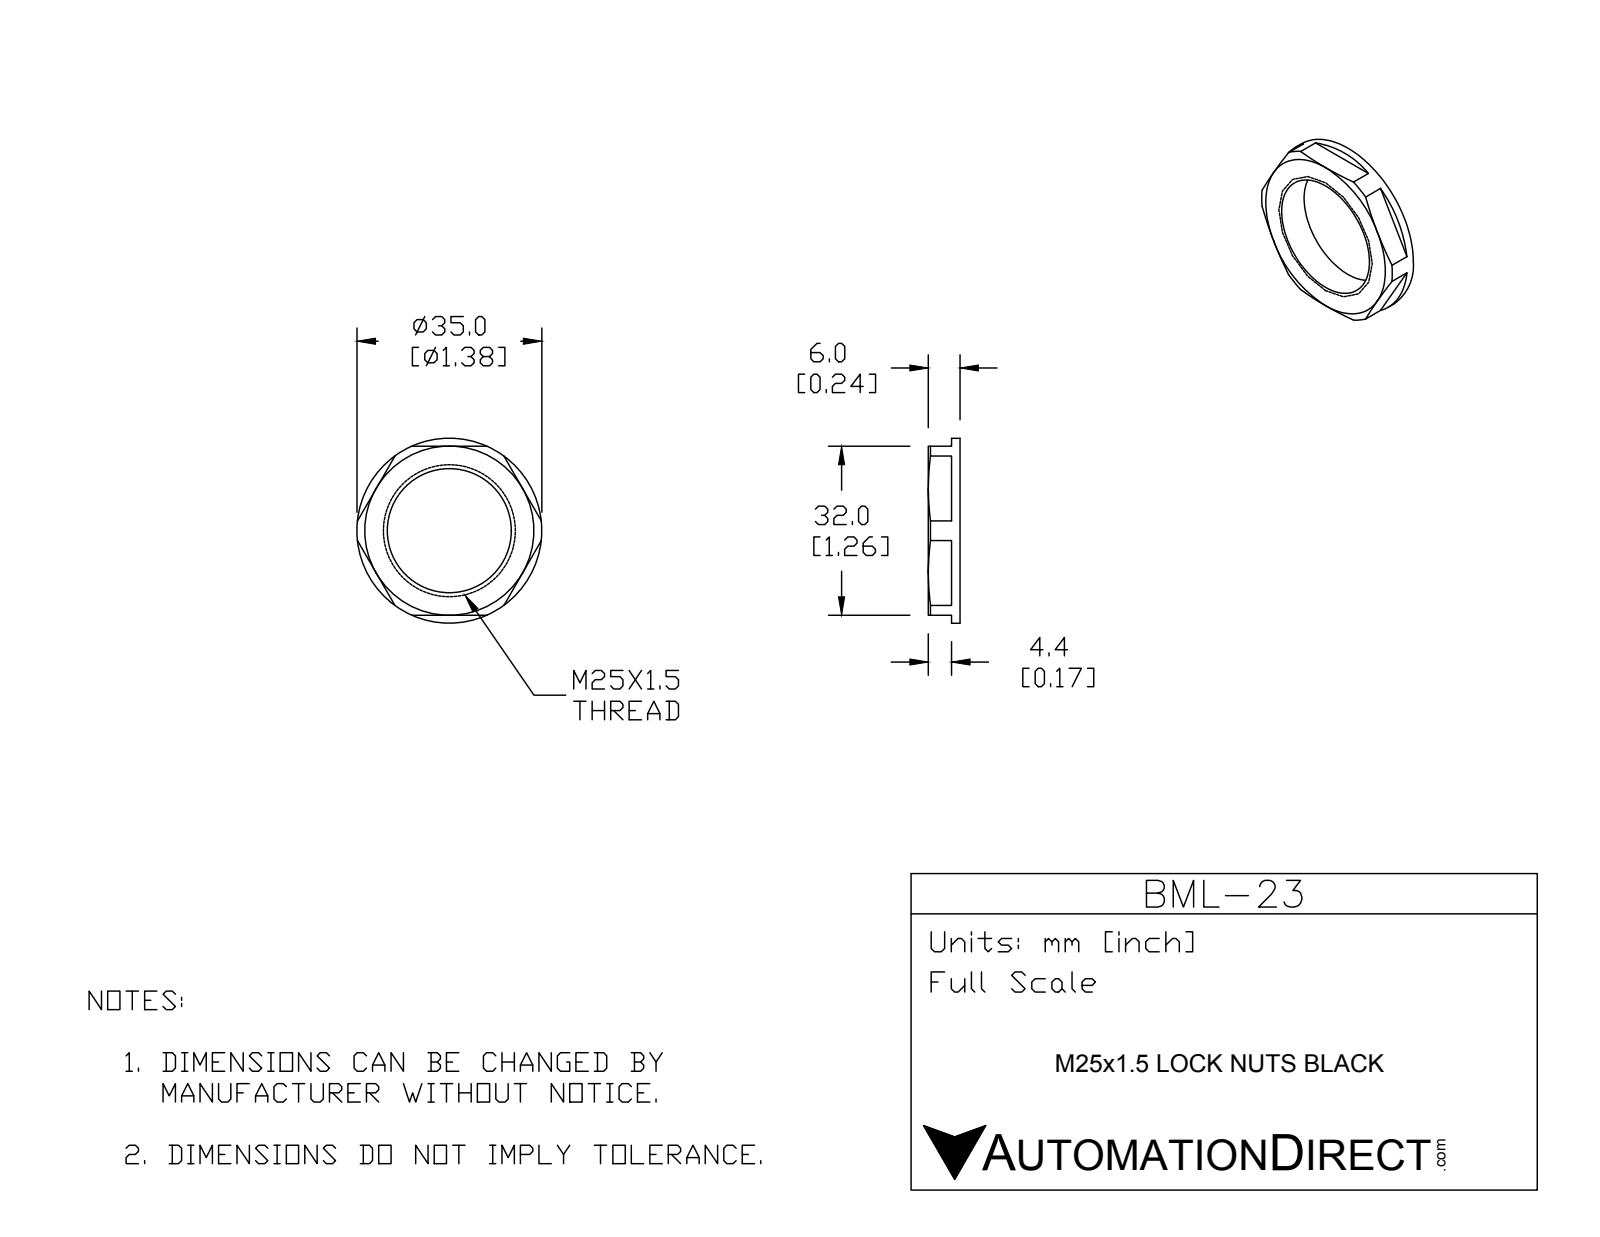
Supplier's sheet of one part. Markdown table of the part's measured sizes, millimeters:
| quantity | value |
| --- | --- |
| part name | BML-23 |
| STEP written by | SolidWorks 2015 (CONFIG_CONTROL_DESIGN) |
| units | millimeters |
| bodies | 1 solid, 33 faces (17 planar, 10 cylindrical, 6 other) |
| overall size | 35 × 35 × 6 |
| volume | 2 780 mm³ |
| surface area | 2 135 mm² |
| round holes (diameter × count) | 1.5 × 3, 23.5 × 1 |
| round bosses / shafts (diameter × count) | 35 × 1 |
| main face-to-face distances | 6, 32, 1.6, 4.4, 1.3, 5.7 |
| hole center spacings | 16.05, 27.8 |
